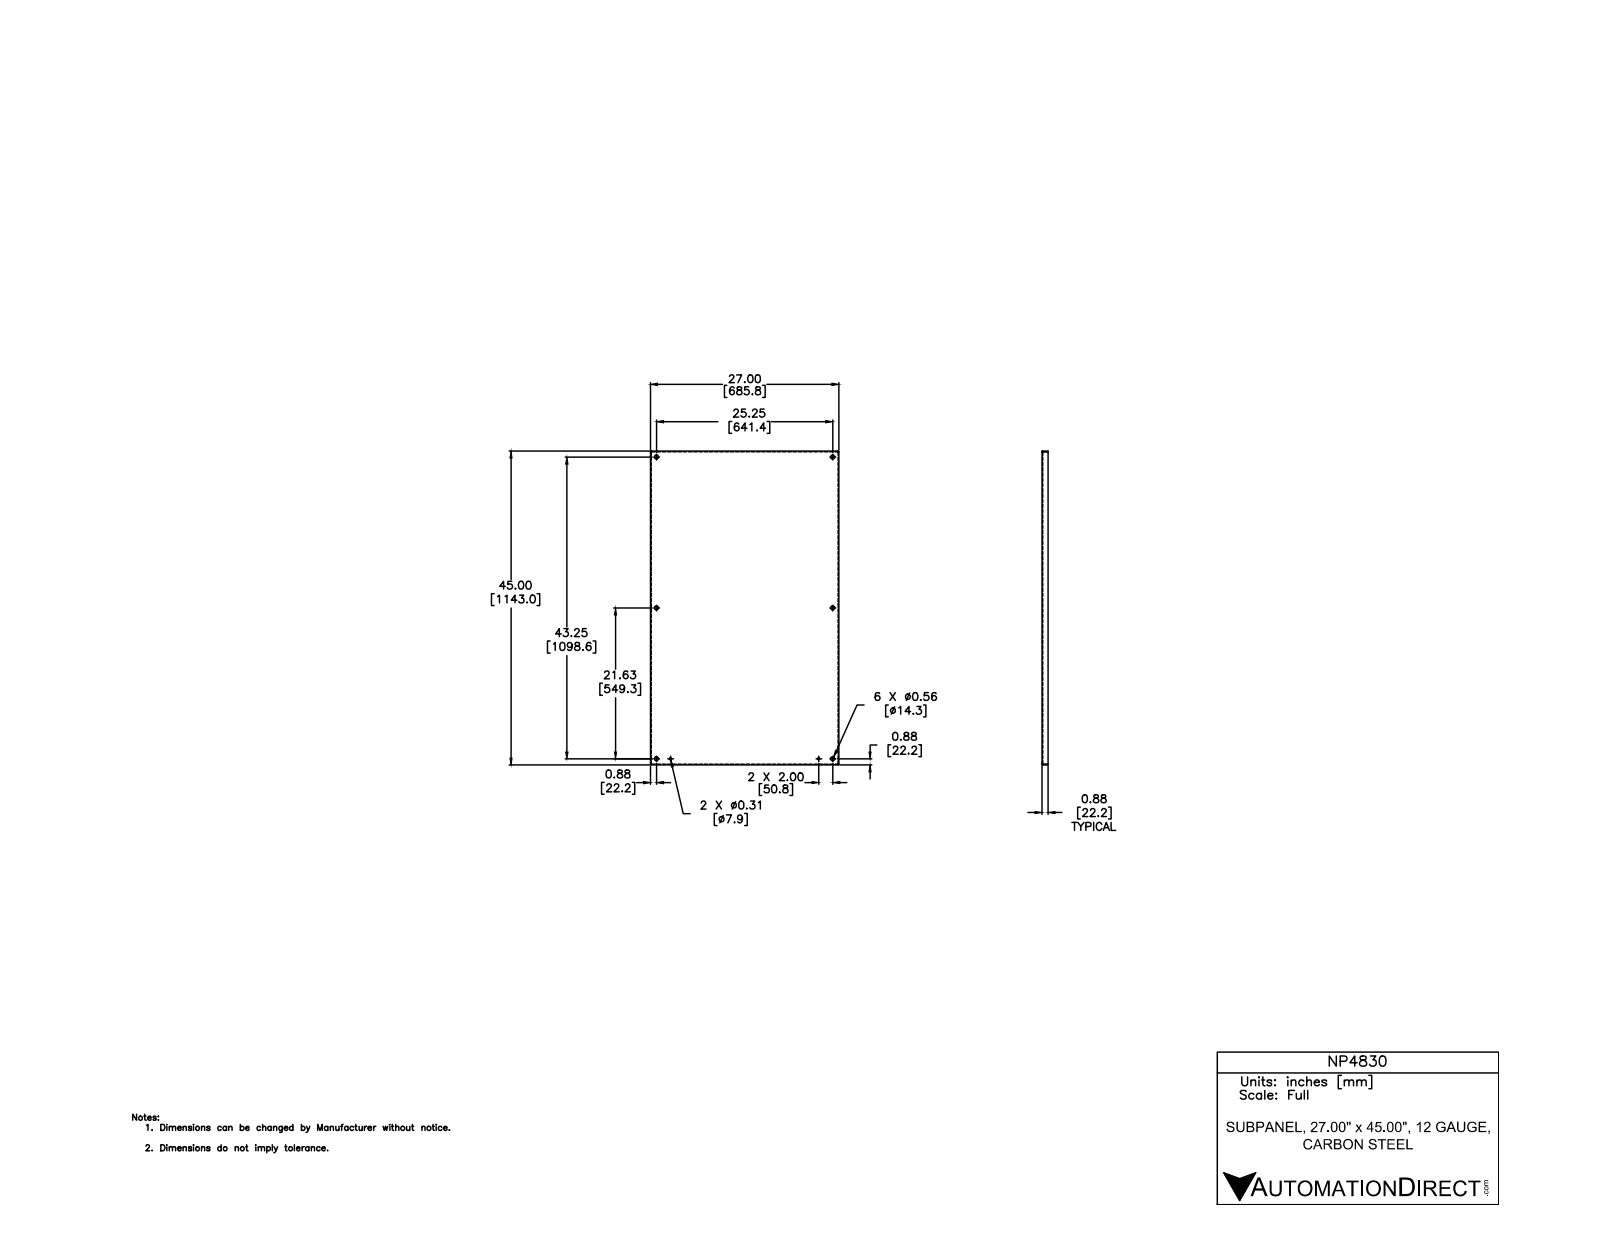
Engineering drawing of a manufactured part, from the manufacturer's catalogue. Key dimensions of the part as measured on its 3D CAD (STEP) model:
Part name (STEP PRODUCT): NP4830
STEP written by: Autodesk Inventor 2012 (AUTOMOTIVE_DESIGN)
Units: inches
Bodies: 1 solid, 46 faces (22 planar, 16 cylindrical, 8 other)
Overall size (bounding box): 45 × 27 × 0.875
Volume: 123.8 in³ · Surface area: 2 656 in²
Round holes (diameter × count): ⌀0.563 ×6, ⌀0.312 ×2
Partial cylindrical surfaces — rounded edges, fillets, slot ends (radius × count): R0.031 ×4, R0.125 ×4
Main face-to-face distances: 0.094, 26.906, 44.906, 27, 26.813, 45, 44.813, 0.781, 0.875, 0.105
Hole centre spacings: 21.625, 33.245, 25.25, 43.25, 43.296, 50.081, 2, 2
